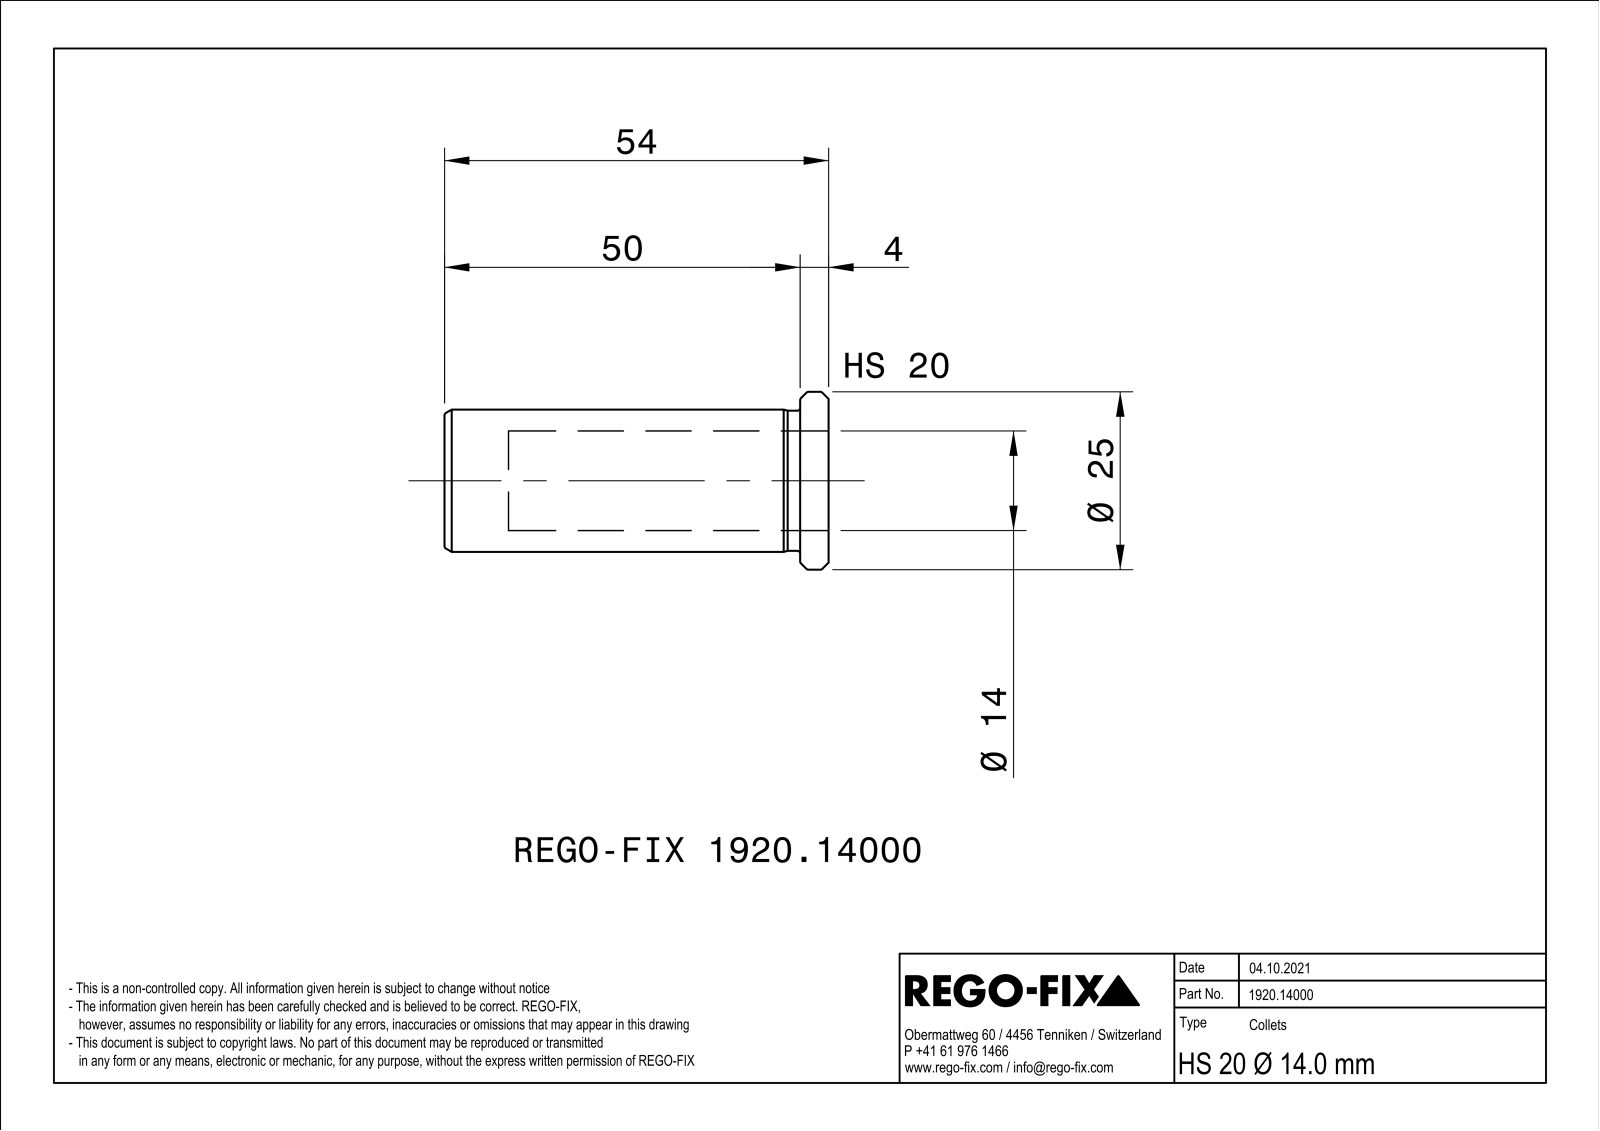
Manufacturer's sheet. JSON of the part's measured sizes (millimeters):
{"part_name": "NOCUT", "step_written_by": "SIEMENS PLM Software Solid Edge ST10 (AUTOMOTIVE_DESIGN)", "units": "millimeters", "bodies": {"solids": 1, "faces": 71, "planar": 22, "cylindrical": 11, "other": 38}, "overall_size": [54, 24.98, 24.98], "volume_mm3": 8347, "surface_area_mm2": 6995, "round_holes": [[14, 1], [16.5, 1]], "round_bosses_or_shafts": [[25, 1], [20, 1], [19.7, 1]], "face_to_face_distances": [1, 4, 54, 50]}
